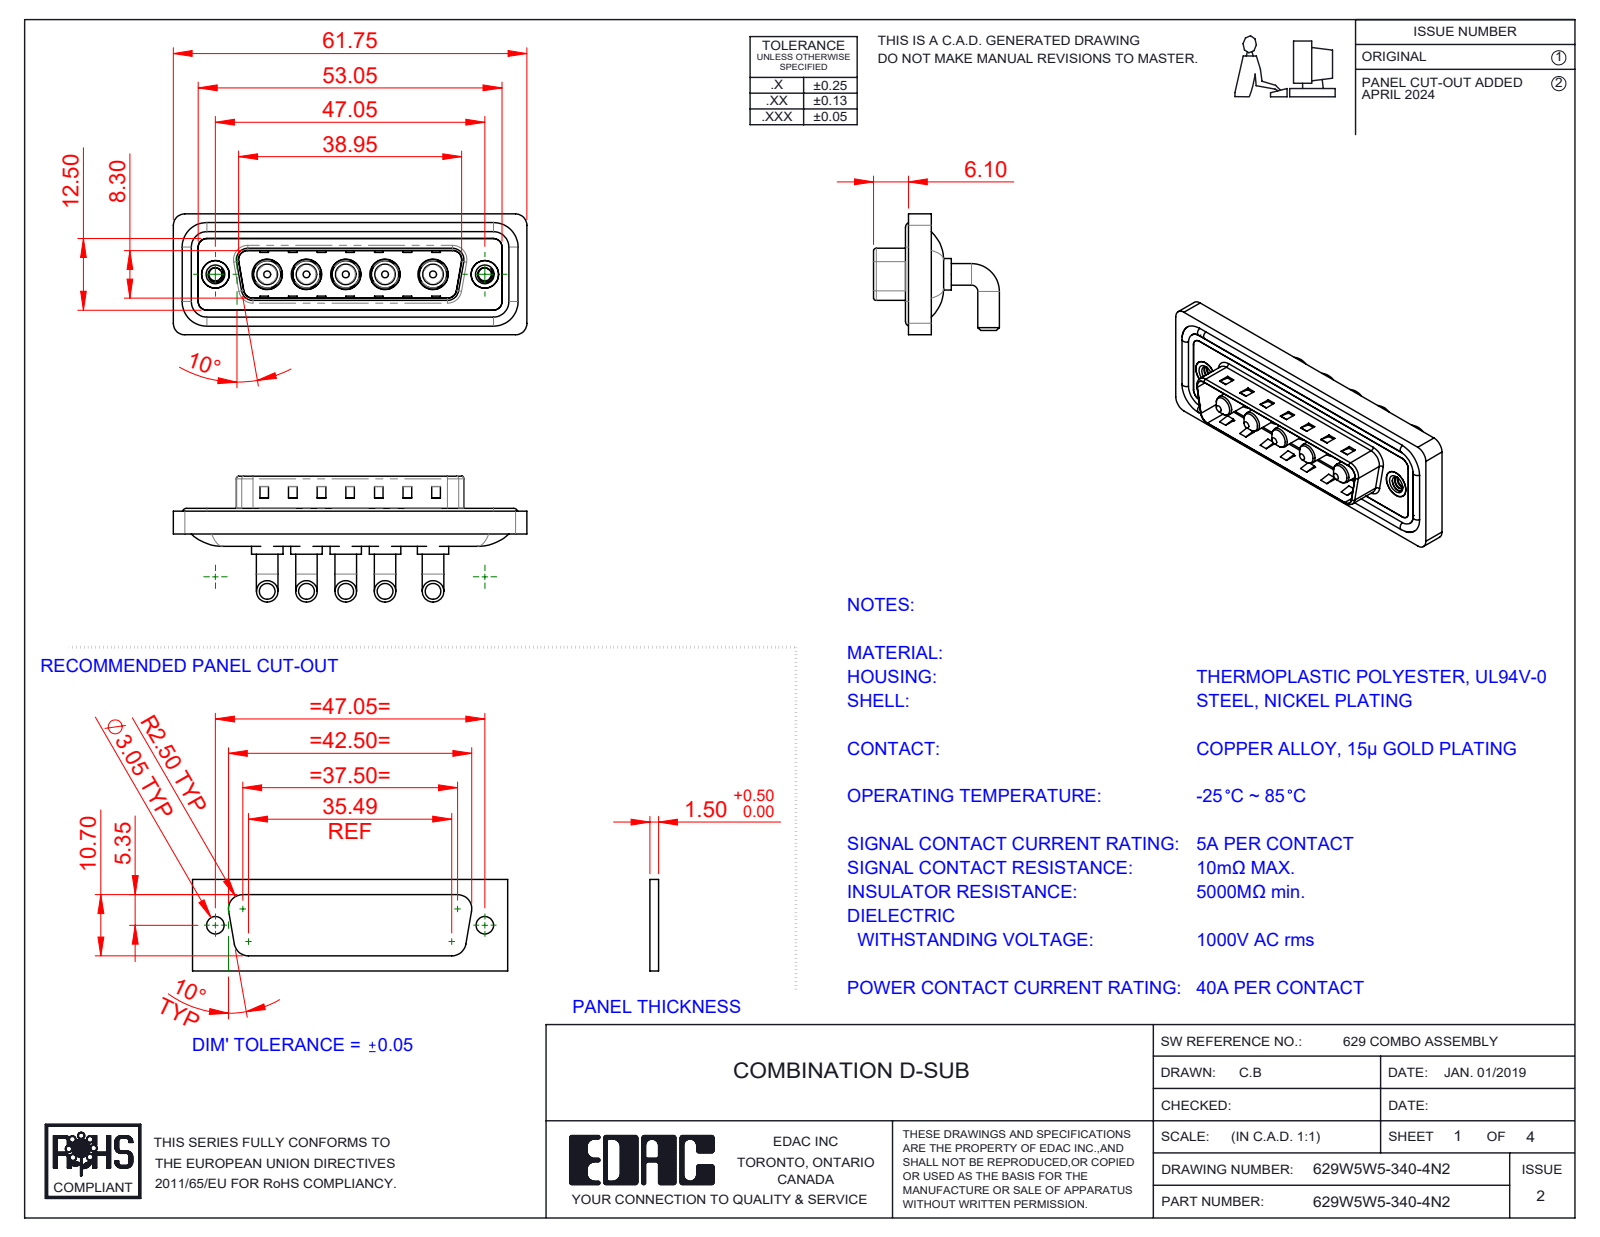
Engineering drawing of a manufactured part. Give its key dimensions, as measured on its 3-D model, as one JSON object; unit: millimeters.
{"part_name": "629Combo Shell Rear_25 Contacts; 629Combo Housing_5W5; 629Combo Shell Front_25 Contacts; 629W5W5-340-4N2 (+3 more)", "step_written_by": "SolidWorks 2023 (CONFIG_CONTROL_DESIGN)", "units": "millimeters", "bodies": {"solids": 17, "faces": 698, "planar": 259, "cylindrical": 293, "other": 146}, "overall_size": [61.75, 21.98, 21.1], "volume_mm3": 8178, "surface_area_mm2": 12492, "round_holes": [[4.85, 5], [5.3, 5], [2.26, 2], [4, 2], [4.8, 2], [5, 2]], "round_bosses_or_shafts": [[3.75, 10], [5.5, 5], [5.2, 5], [4.75, 5], [3.6, 5], [1.6, 4], [4.9, 2]], "partial_cylinders_radius": [[1.5, 18], [2, 18], [0.5, 8], [1.6, 8], [2.1, 5], [0.25, 4], [0.6, 4], [0.65, 4]], "face_to_face_distances": [0.4, 2.9, 0.8, 4.5, 4.1, 1.1, 2.1, 3.1, 6, 2.5], "hole_center_spacings": [6.86, 13.73, 6.85, 6.87, 8.37, 8.38, 9.04, 9.05]}
